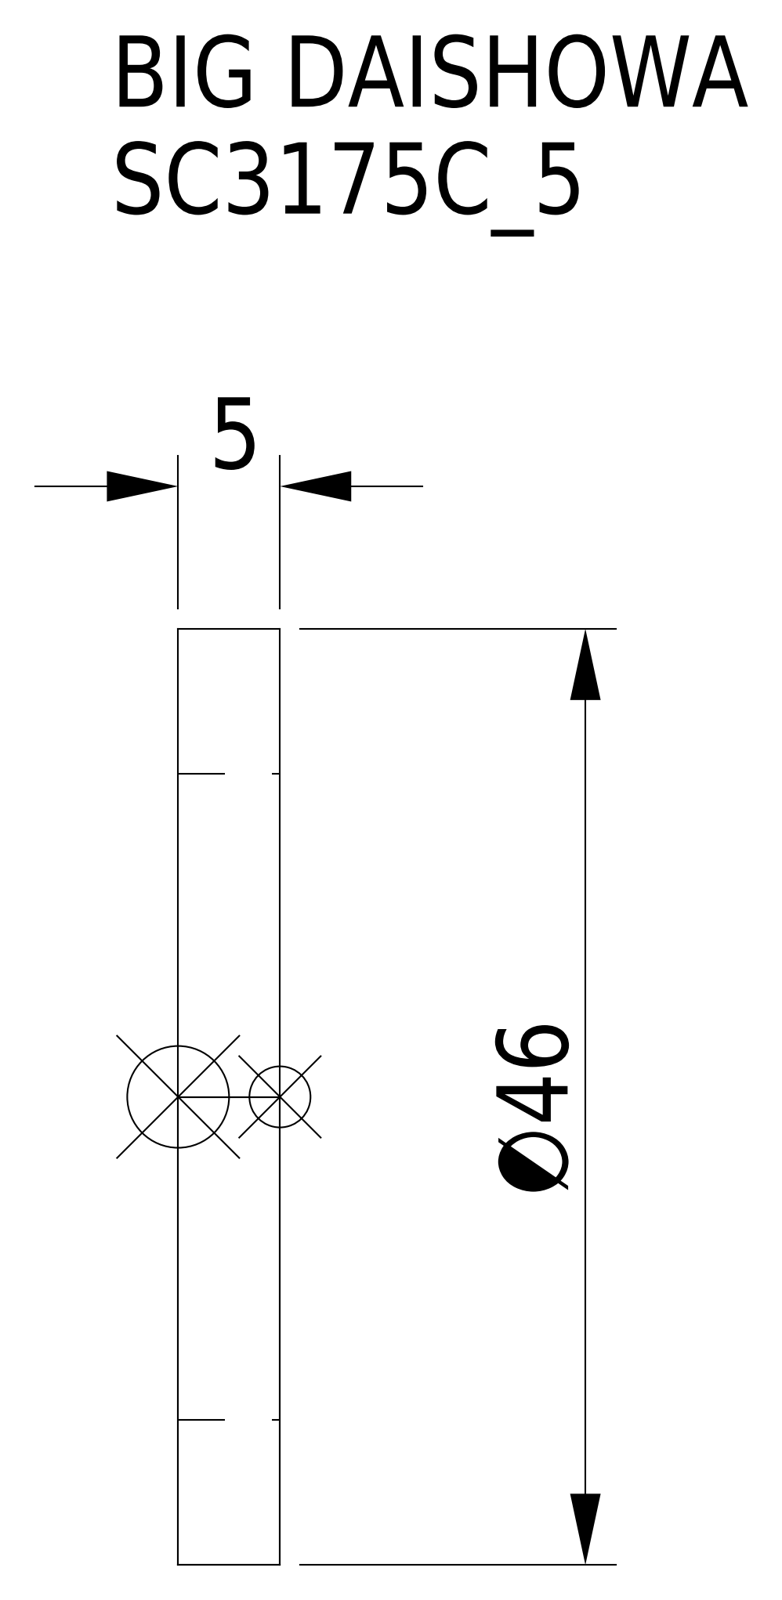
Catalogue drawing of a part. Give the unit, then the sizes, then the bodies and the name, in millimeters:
Units: millimetres
Overall size (bounding box): 46 × 46 × 5
Round holes (diameter × count): ⌀31.75 ×1
Round bosses / shafts (diameter × count): ⌀46 ×1
Main face-to-face distances: 5, 8.1
Volume: 4 204 mm³ · Surface area: 2 942 mm²
Bodies: 1 solid, 8 faces (5 planar, 3 cylindrical, 0 other)
Part name (STEP PRODUCT): SC3175C_5
STEP written by: CREO PARAMETRIC BY PTC INC, 2016380 (AUTOMOTIVE_DESIGN)
